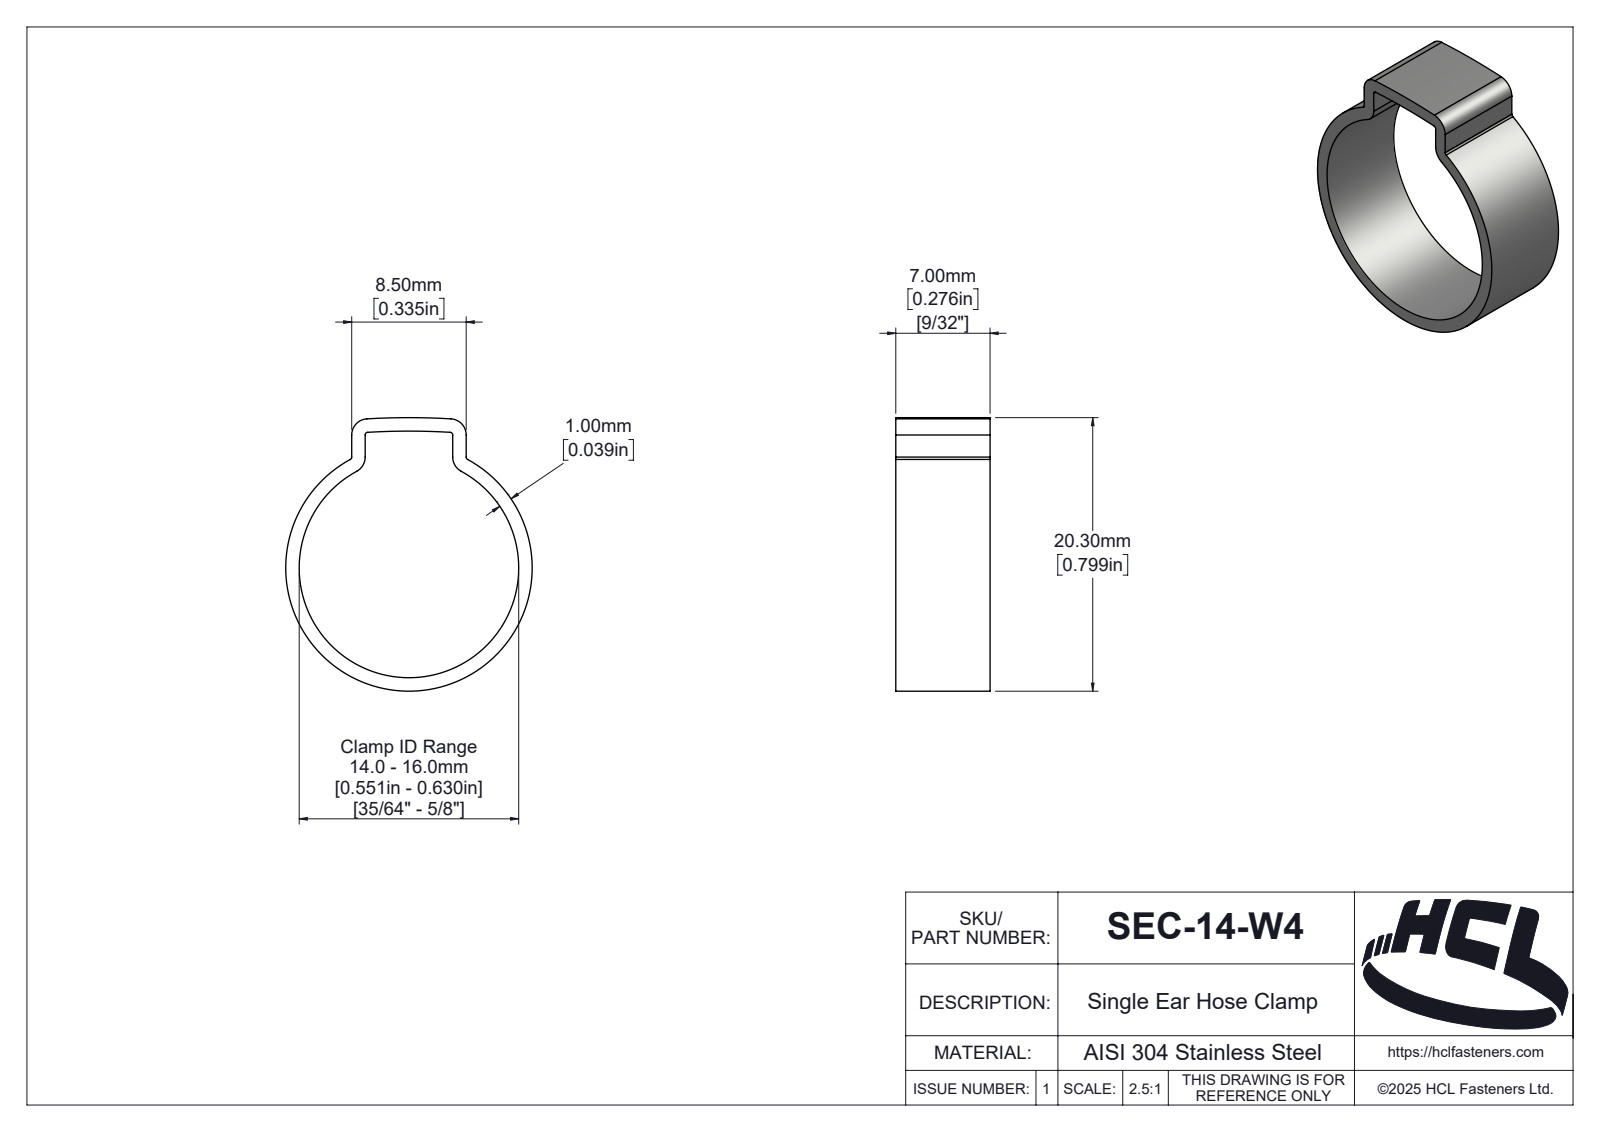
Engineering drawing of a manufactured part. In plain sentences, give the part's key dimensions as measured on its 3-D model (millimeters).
The part is named "SEC-14-W4". Its 3-D file was written by "SolidWorks 2025 (AUTOMOTIVE_DESIGN)". It is 1 solid with 123 faces: 8 planar, 66 cylindrical and 49 other. Overall it measures 20.3 by 18.3 by 7 millimeters. Its volume is 411 cubic millimeters and its surface area 945 square millimeters. Round holes: 1 of diameter 16.3. Round bosses or shafts: 1 of diameter 18.3. Partial cylindrical surfaces (rounded edges, fillets, slot ends): 4 of radius 0.2, 4 of radius 1.2, 1 of radius 0.2, 1 of radius 0.81, 1 of radius 1.01, 1 of radius 1.06, 1 of radius 1.28, 1 of radius 1.81. The main face-to-face distances are 7, 1, 7.5, 8.5, 6.5, 3.98, 2.98, 3.52, 4.52, 4.13.
